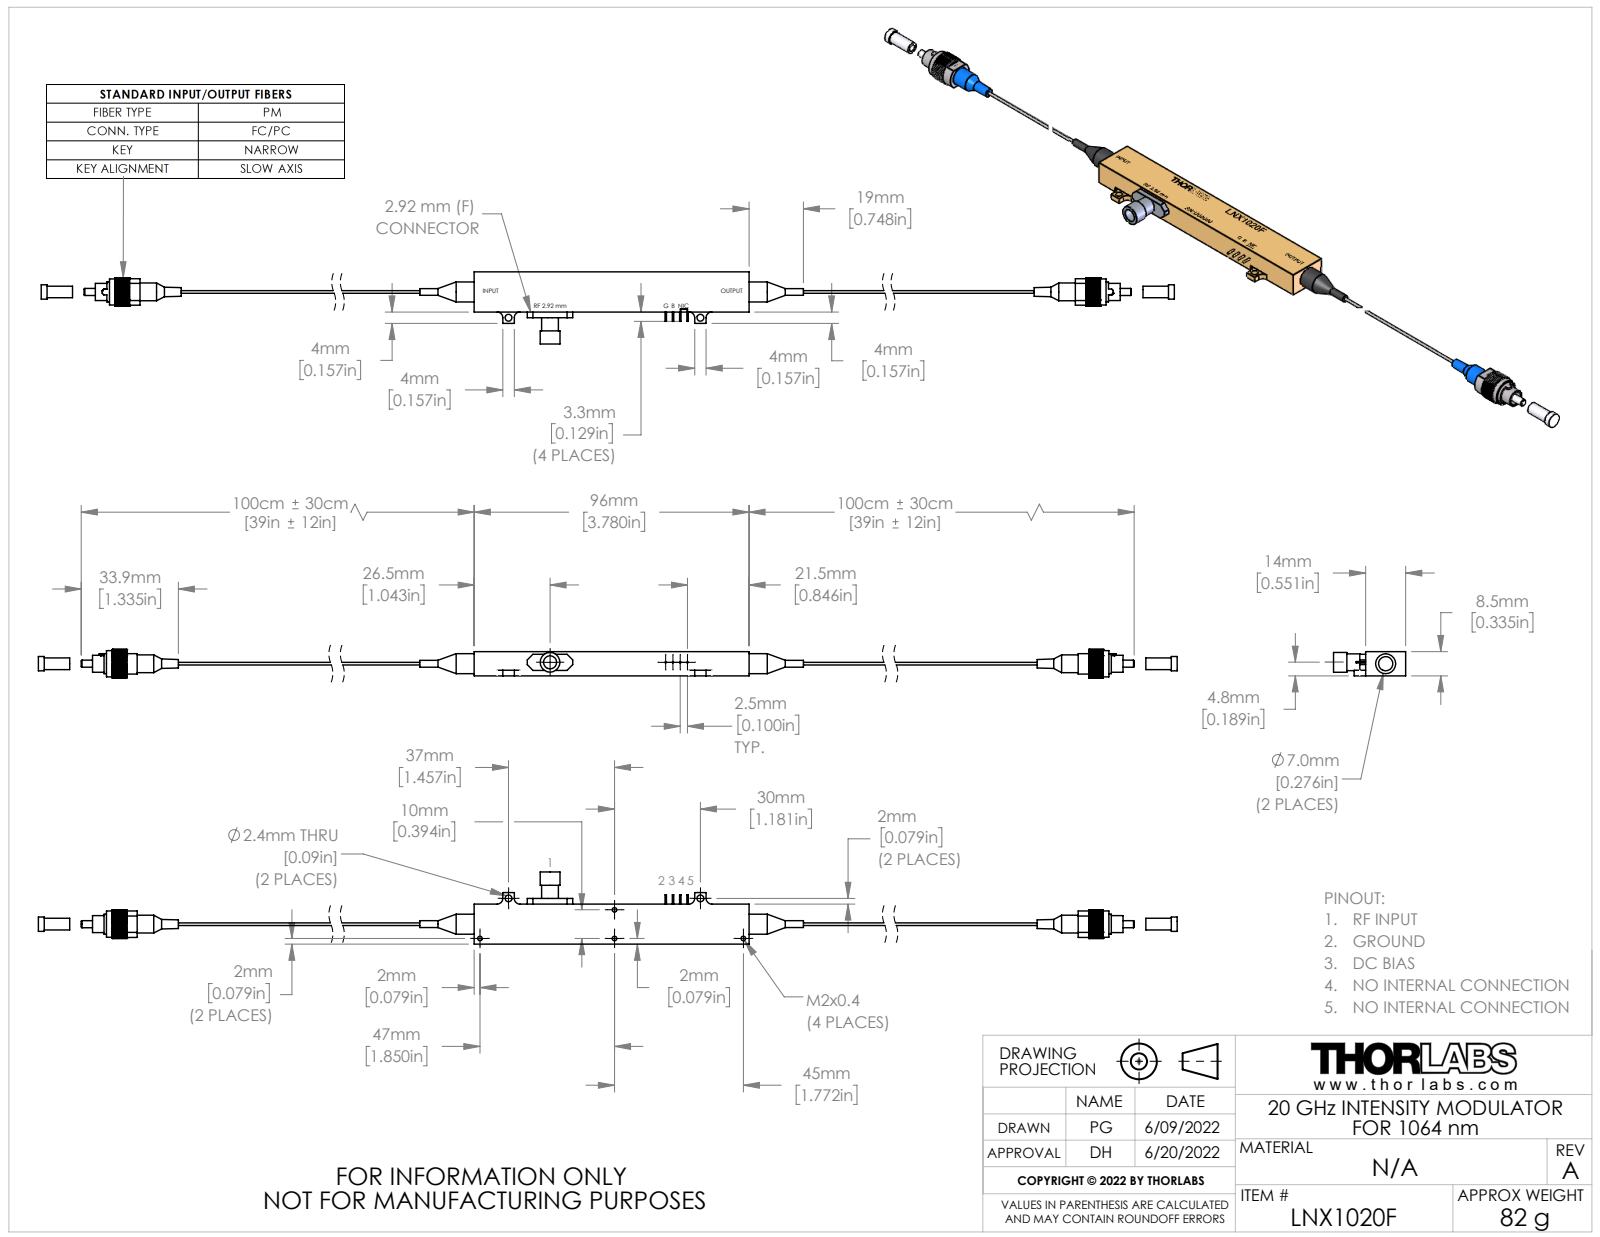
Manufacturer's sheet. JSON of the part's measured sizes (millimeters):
{"part_name": "OHW-00233_LNX1020F; Thorlabs CAPF; LNX1020F; Thorlabs 30125D2_900um Boot", "step_written_by": "SolidWorks 2018 (AUTOMOTIVE_DESIGN)", "units": "millimeters", "bodies": {"solids": 9, "faces": 553, "planar": 277, "cylindrical": 248, "other": 28}, "overall_size": [472.7, 25.2, 10], "volume_mm3": 14900, "surface_area_mm2": 10410, "round_holes": [[1.6, 4], [2.4, 2], [1.1, 1], [1.4, 1], [2.5, 1], [3.8, 1], [4.6, 1], [4.9, 1], [5, 1], [6.4, 1], [6.5, 1], [8.3, 1]], "round_bosses_or_shafts": [[0.5, 4], [7, 1], [7, 1], [6.9, 1], [6.2, 1], [5.9, 1], [5.8, 1], [5, 1]], "partial_cylinders_radius": [[0.2, 8], [2, 4], [4.6, 1], [5, 1]], "face_to_face_distances": [8.5, 14, 2, 157.6, 253.6, 6.8, 96, 7.9, 411.1, 0.8], "hole_center_spacings": [10, 17.2, 20.5, 30.3, 33.1, 37.2, 39.5, 45]}
